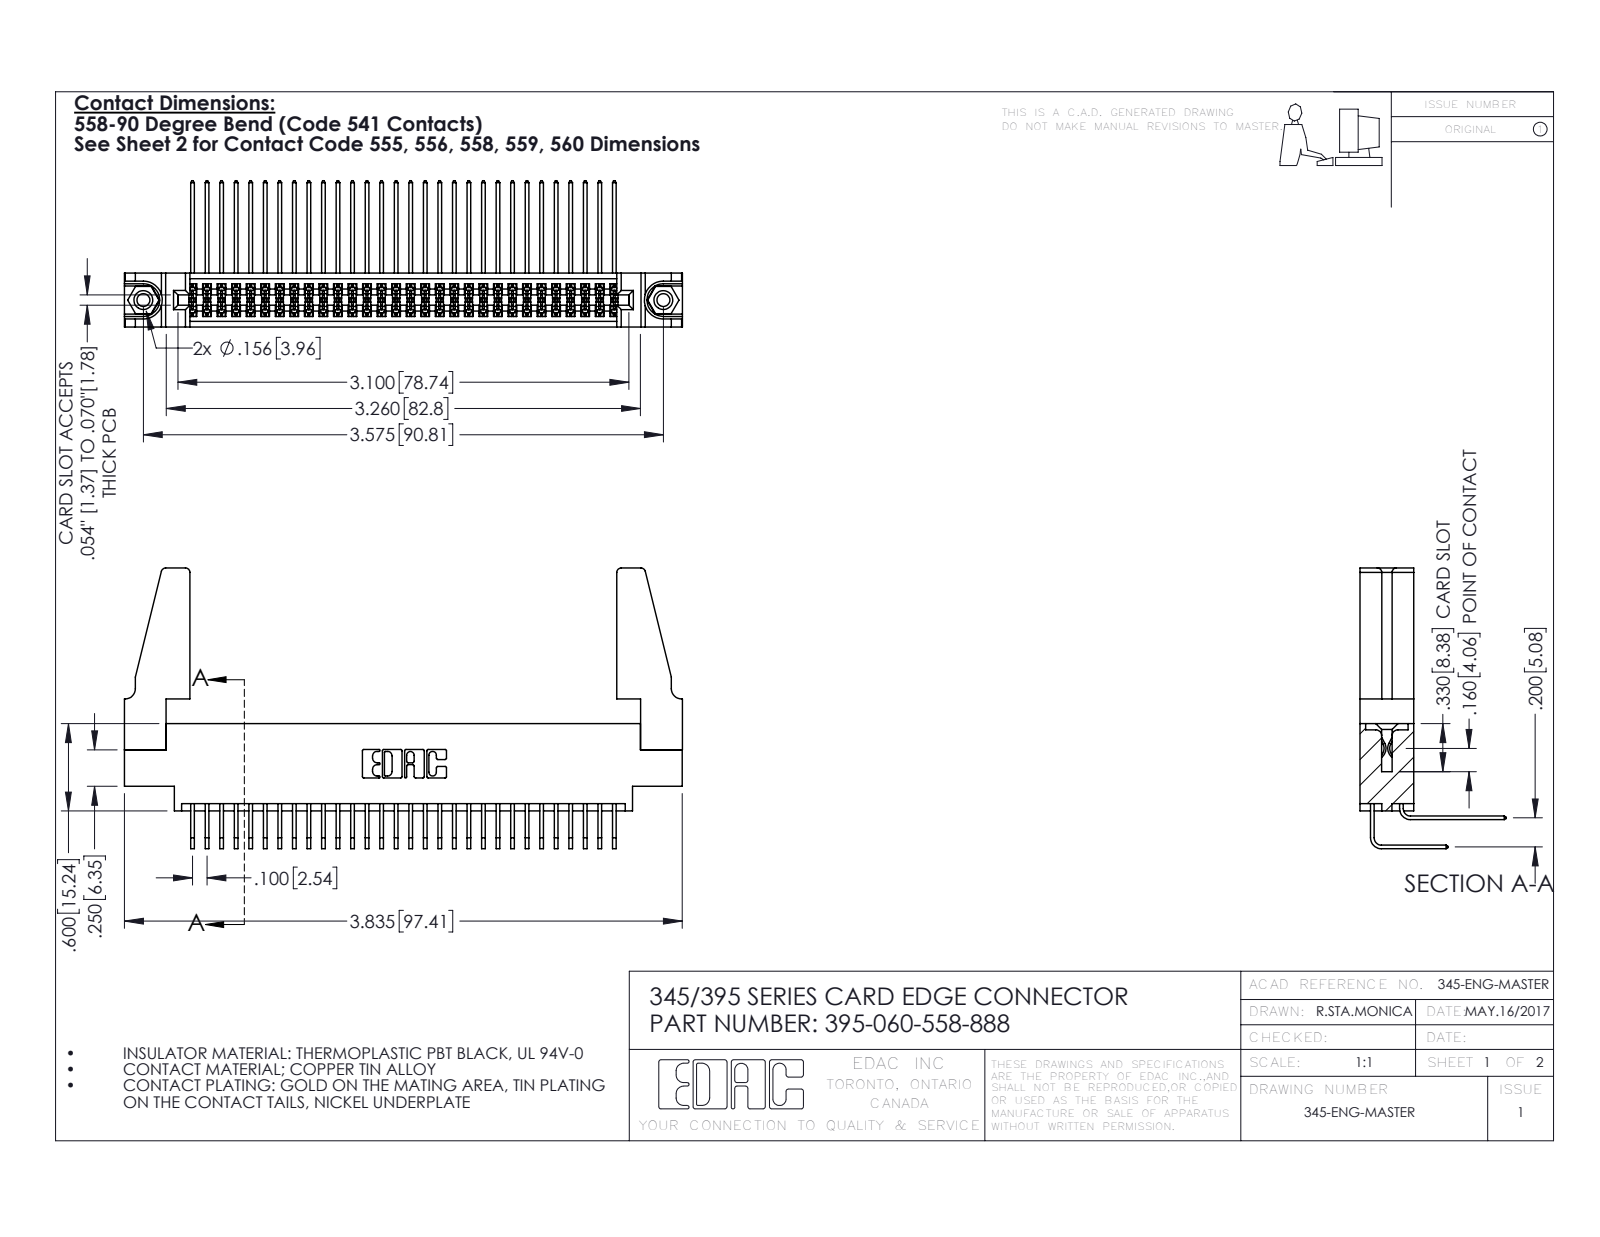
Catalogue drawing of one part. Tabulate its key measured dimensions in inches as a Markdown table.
| quantity | value |
| --- | --- |
| part name | 345-220-078_345-220-088; 395-060-558-888; 345 Part_0.170 Offset - 0.156 Dia-TH; 345-292-001_558 559 Tail - 1 (+2 more) |
| STEP written by | SolidWorks 2016 (CONFIG_CONTROL_DESIGN) |
| units | inches |
| bodies | 65 solids, 3374 faces (2256 planar, 1102 cylindrical, 16 other) |
| overall size | 3.836 × 1.929 × 1.005 |
| volume | 0.783 in³ |
| surface area | 29.19 in² |
| round holes (diameter × count) | 0.089 × 2, 0.125 × 2, 0.156 × 2, 0.064 × 1 |
| round bosses / shafts (diameter × count) | 0.155 × 2 |
| partial cylindrical surfaces (radius × count) | 0.006 × 91, 0.01 × 22, 0.03 × 8, 0.007 × 6, 0.031 × 6, 0.026 × 3, 0.014 × 2, 0.019 × 2 |
| main face-to-face distances | 0.072, 0.298, 0.37, 0.2, 0.098, 0.272, 0.025, 0.225, 0.175, 0.025 |
| hole center spacings | 0.27, 3.34, 3.575 |
